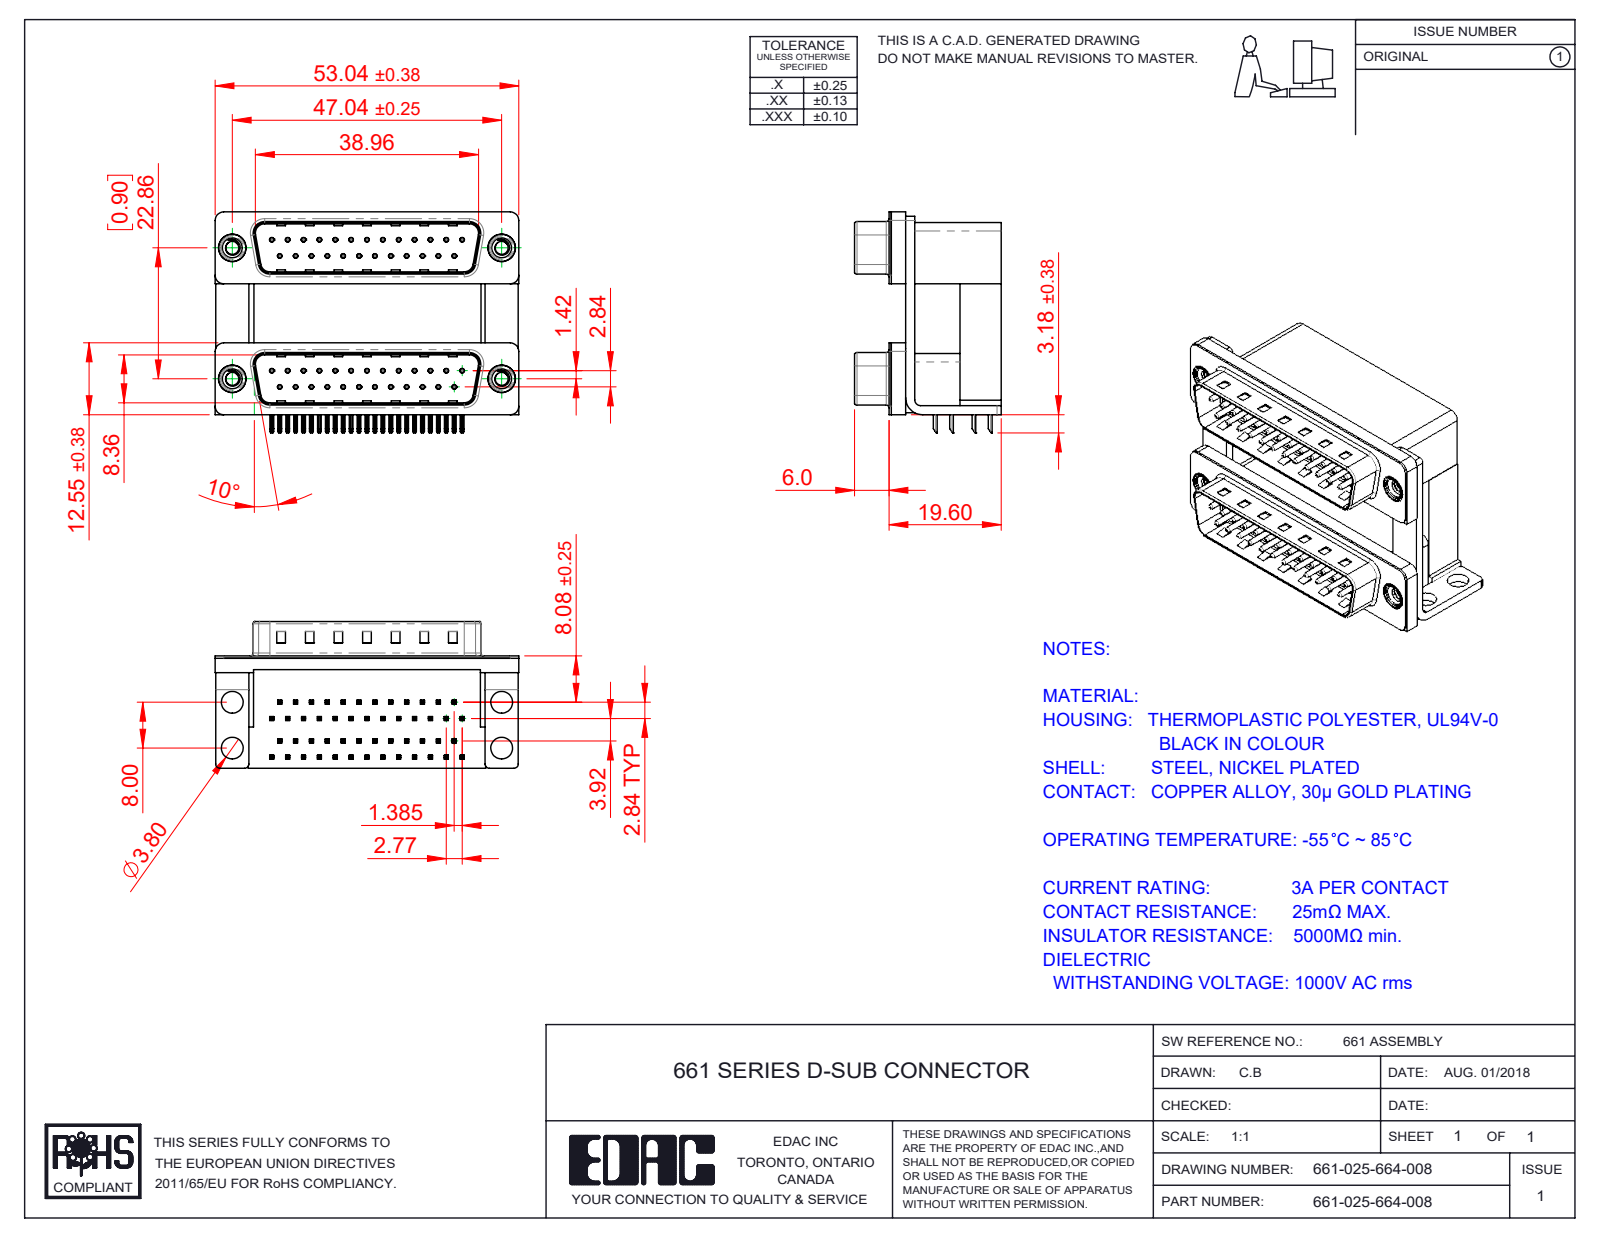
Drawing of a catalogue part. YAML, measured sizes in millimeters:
part_name: "661 Contact Top Upper_H; 661 Contact Bottom Lower; 661 Contact Bottom Upper_H; 661 Mounting Bracket_NoneH (+7 more)"
step_written_by: "SolidWorks 2020 (CONFIG_CONTROL_DESIGN)"
units: millimeters
bodies: {solids: 61, faces: 4594, planar: 2934, cylindrical: 1266, other: 394}
overall_size: [53.04, 38.59, 25.6]
volume: 22154
surface_area: 22696
round_holes:
  - {diameter: 0.35, count: 50}
  - {diameter: 0.8, count: 50}
  - {diameter: 2.26, count: 4}
  - {diameter: 3.5, count: 4}
  - {diameter: 4, count: 4}
  - {diameter: 4.8, count: 4}
  - {diameter: 5, count: 4}
round_bosses_or_shafts:
  - {diameter: 0.75, count: 50}
  - {diameter: 4.9, count: 4}
  - {diameter: 4.75, count: 4}
  - {diameter: 3.9, count: 4}
partial_cylinders:
  - {radius: 0.25, count: 200}
  - {radius: 0.12, count: 100}
  - {radius: 0.5, count: 16}
  - {radius: 1.5, count: 14}
  - {radius: 0.9, count: 8}
  - {radius: 1.6, count: 8}
  - {radius: 2, count: 8}
  - {radius: 0.4, count: 4}
face_to_face_distances: [12, 19.2, 0.4, 22.86, 7.2, 16.7, 9.5, 2.5, 12.4, 10.7]
hole_center_spacings: [2.77, 3.16, 5.54, 8.31, 11.08, 13.85, 16.62, 5.03]
